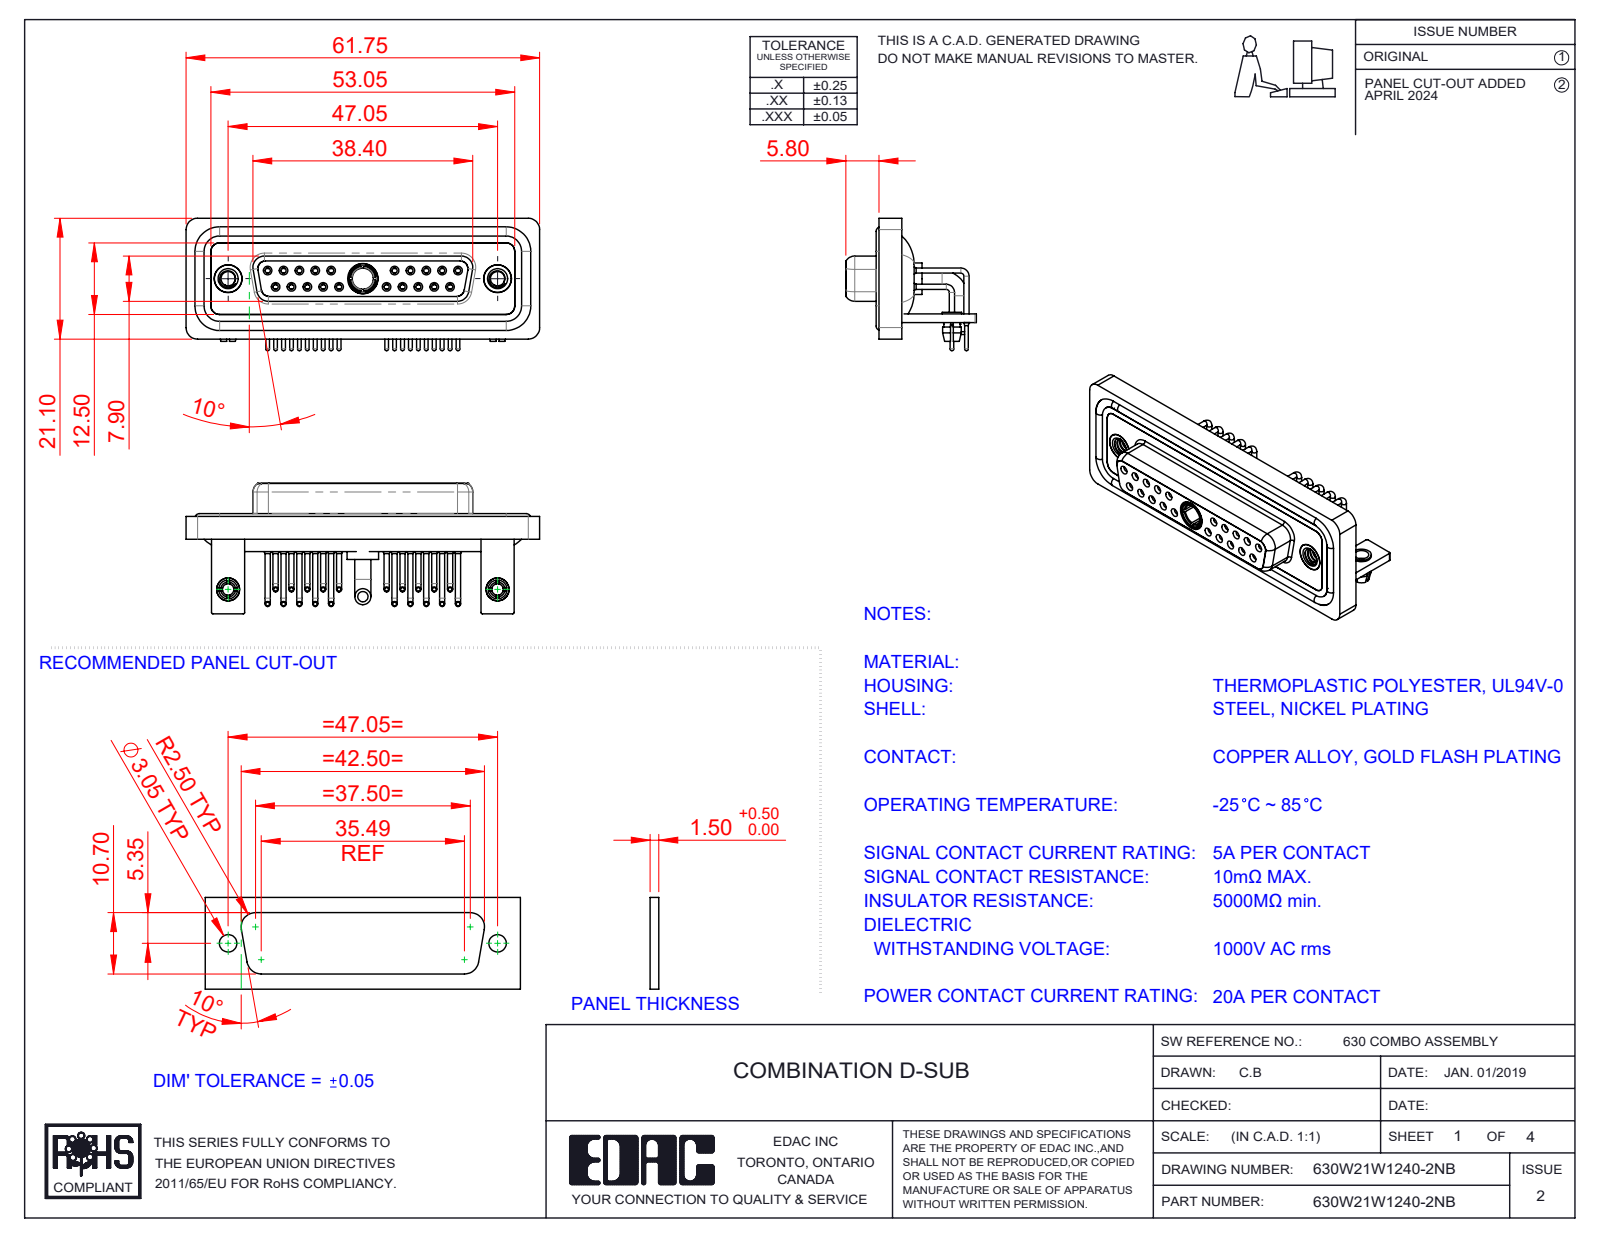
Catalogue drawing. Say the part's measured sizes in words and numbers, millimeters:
The part is named "630Combo Contact Row 1_50 Contacts; 630Combo Waterproof Housing_25 Contacts; 630Combo Board Lock_50 Contacts; 630W21W1240-2NB (+7 more)". Its 3-D file was written by "SolidWorks 2023 (CONFIG_CONTROL_DESIGN)". It is 33 solids with 1658 faces: 502 planar, 727 cylindrical and 429 other. Overall it measures 61.75 by 23.12 by 22.8 millimeters. Its volume is 8 901 cubic millimeters and its surface area 15 729 square millimeters. Round holes: 22 of diameter 2, 20 of diameter 0.9, 20 of diameter 1.1, 20 of diameter 1.5, 10 of diameter 1.6, 10 of diameter 1.7, 4 of diameter 2.5, 3 of diameter 4.85, 2 of diameter 3.2, 2 of diameter 4, 2 of diameter 4.05, 2 of diameter 5. Round bosses or shafts: 20 of diameter 0.9, 20 of diameter 0.65, 14 of diameter 1.6, 2 of diameter 4.95, 2 of diameter 4.8, 2 of diameter 4, 2 of diameter 3.4, 2 of diameter 3.3. Partial cylindrical surfaces (rounded edges, fillets, slot ends): 19 of radius 2, 18 of radius 1.5, 16 of radius 0.25, 8 of radius 1.35, 8 of radius 1.6, 5 of radius 0.5, 4 of radius 0.6, 4 of radius 0.65. The main face-to-face distances are 0.4, 1.8, 2.9, 3.7, 1.5, 4.1, 1.1, 1.4, 1.6, 2.5. The hole center spacings are 3.16, 2.77, 5.54, 8.31, 5.04, 19.39, 20.97, 22.16.
